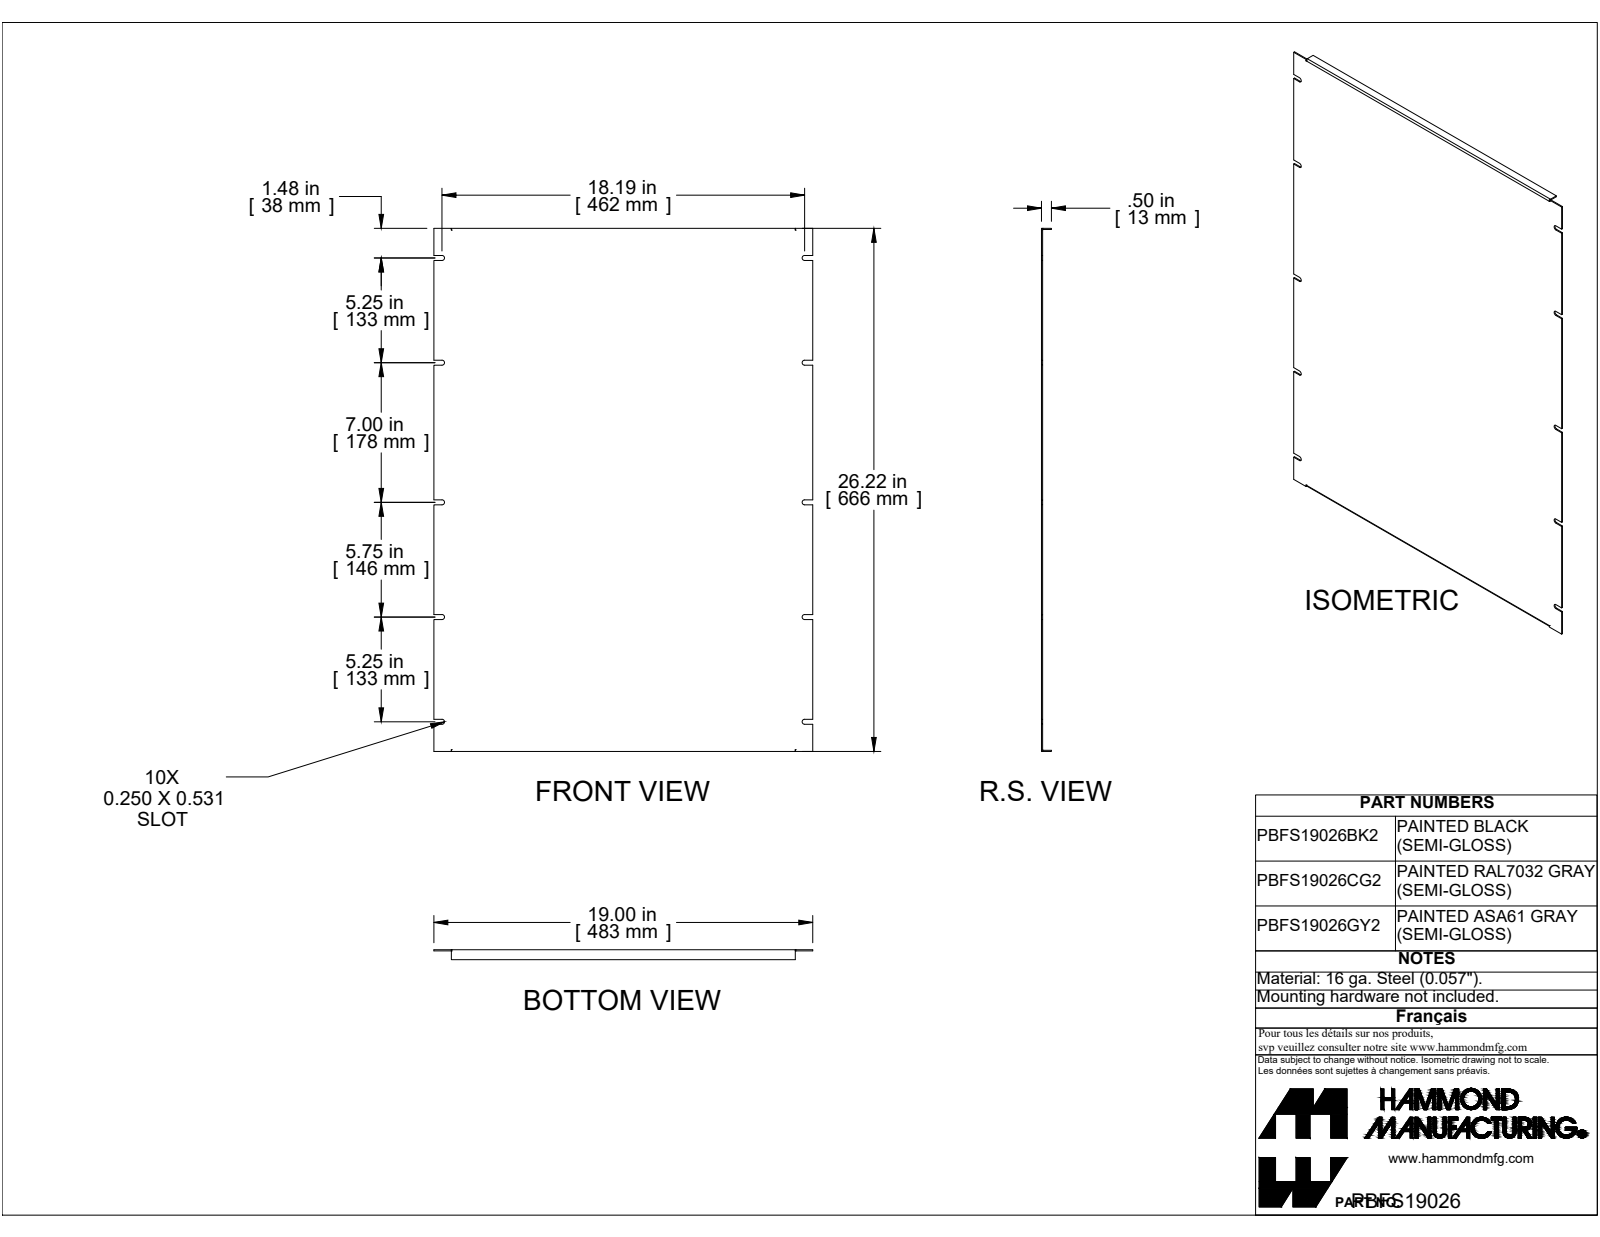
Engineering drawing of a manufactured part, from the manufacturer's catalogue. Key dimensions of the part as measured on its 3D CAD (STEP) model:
Part name (STEP PRODUCT): PBFS19026
STEP written by: SolidWorks 2019 (CONFIG_CONTROL_DESIGN)
Units: inches
Bodies: 1 solid, 70 faces (56 planar, 14 cylindrical, 0 other)
Overall size (bounding box): 26.218 × 19 × 0.5
Volume: 29.14 in³ · Surface area: 1 028 in²
Partial cylindrical surfaces — rounded edges, fillets, slot ends (radius × count): R0.125 ×10, R0.029 ×2, R0.086 ×2
Main face-to-face distances: 0.057, 26.161, 26.218, 26.104, 0.5, 0.443, 19, 0.25, 5.25, 18
